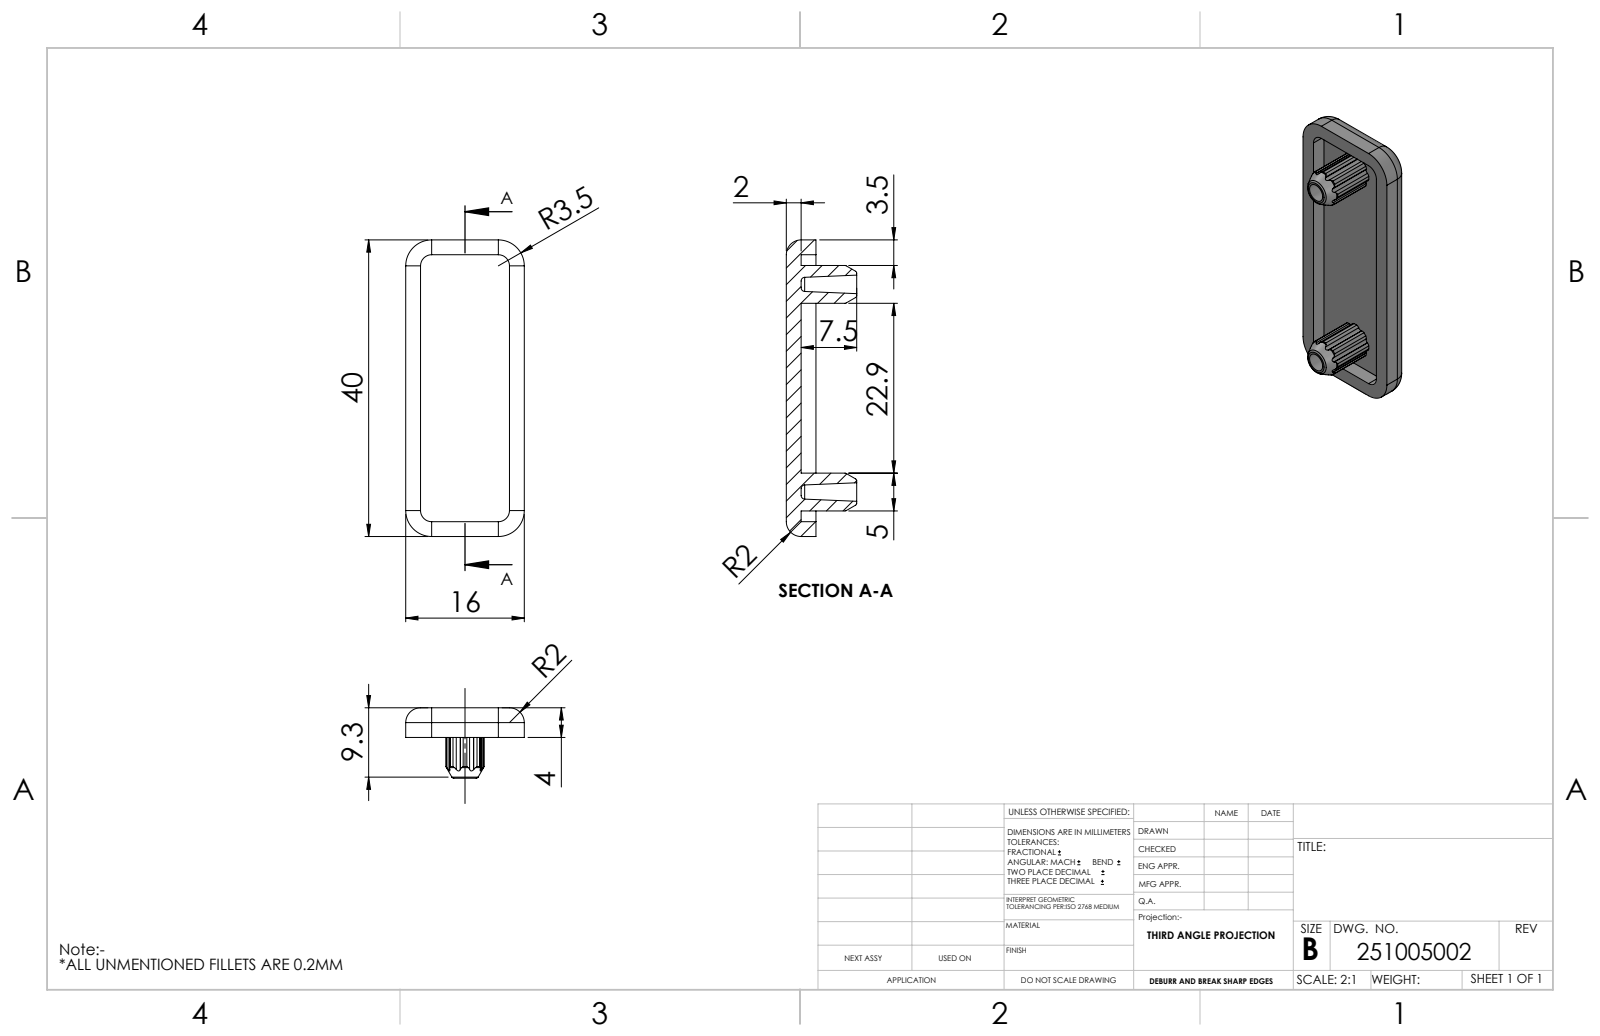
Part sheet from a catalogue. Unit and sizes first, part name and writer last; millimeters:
Units: millimetres
Overall size (bounding box): 40 × 16 × 9.5
Partial cylindrical surfaces — rounded edges, fillets, slot ends (radius × count): R0.49 ×48, R1.5 ×4, R2 ×4, R3.5 ×4, R2.55 ×2
Main face-to-face distances: 2, 4, 14, 12, 16, 38, 40, 36, 5.5, 7.5
Volume: 1 780 mm³ · Surface area: 2 098 mm²
Bodies: 1 solid, 135 faces (31 planar, 76 cylindrical, 28 other)
Part name (STEP PRODUCT): 251005002 Abdeckkappe 16x40
STEP written by: Autodesk Inventor 2019 (AUTOMOTIVE_DESIGN)
